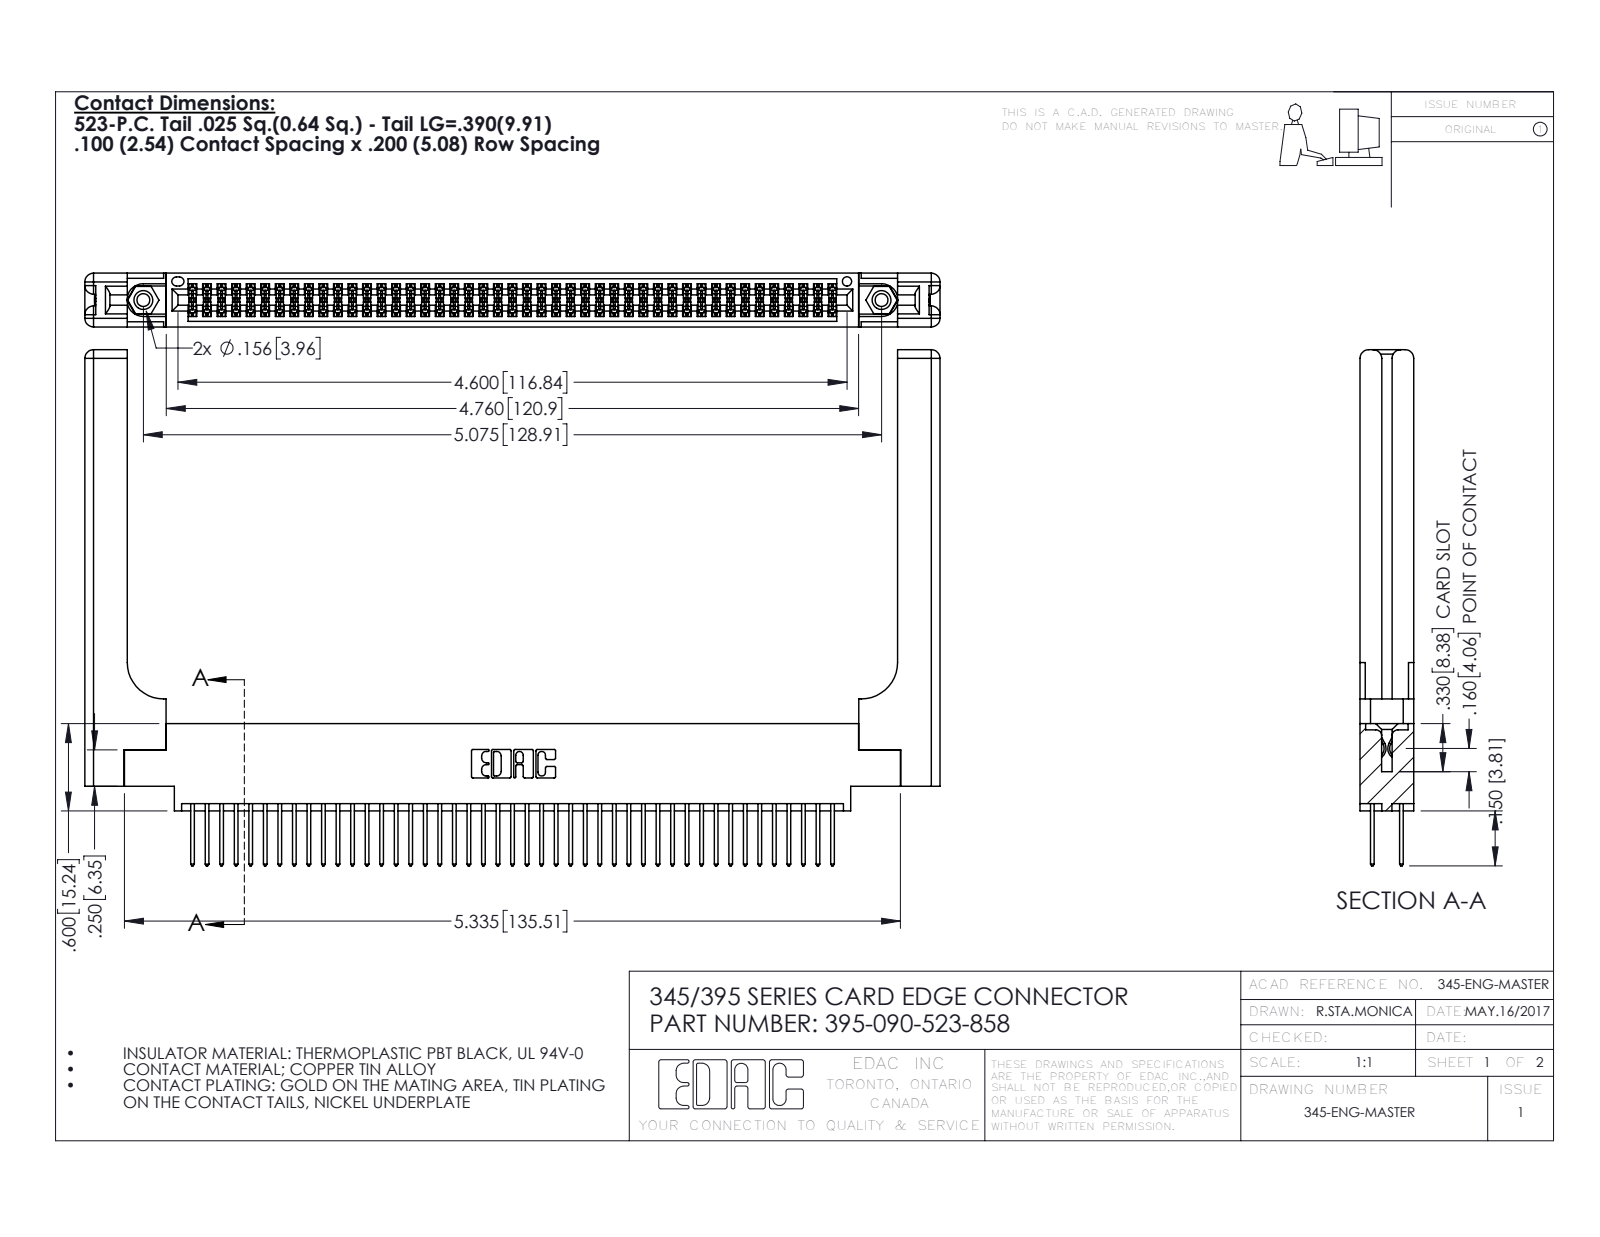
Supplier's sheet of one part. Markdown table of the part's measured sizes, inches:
| quantity | value |
| --- | --- |
| part name | 345-250-001_345-250-001-102; 395-090-523-858; 345-292-001_345-293-123; 345 Part_0.170 Offset - 0.156 Dia-TH (+1 more) |
| STEP written by | SolidWorks 2016 (CONFIG_CONTROL_DESIGN) |
| units | inches |
| bodies | 95 solids, 4886 faces (3202 planar, 1624 cylindrical, 60 other) |
| overall size | 5.879 × 3.547 × 0.37 |
| volume | 1.408 in³ |
| surface area | 42.9 in² |
| round holes (diameter × count) | 0.089 × 2, 0.125 × 2, 0.156 × 2, 0.064 × 1 |
| round bosses / shafts (diameter × count) | 0.155 × 2 |
| partial cylindrical surfaces (radius × count) | 0.006 × 135, 0.01 × 90, 0.01 × 22, 0.06 × 16, 0.007 × 6, 0.031 × 6, 0.026 × 3, 0.014 × 2 |
| main face-to-face distances | 0.072, 0.298, 0.37, 0.098, 0.272, 0.025, 0.2, 0.225, 0.175, 0.148 |
| hole center spacings | 0.27, 4.839, 5.075 |
